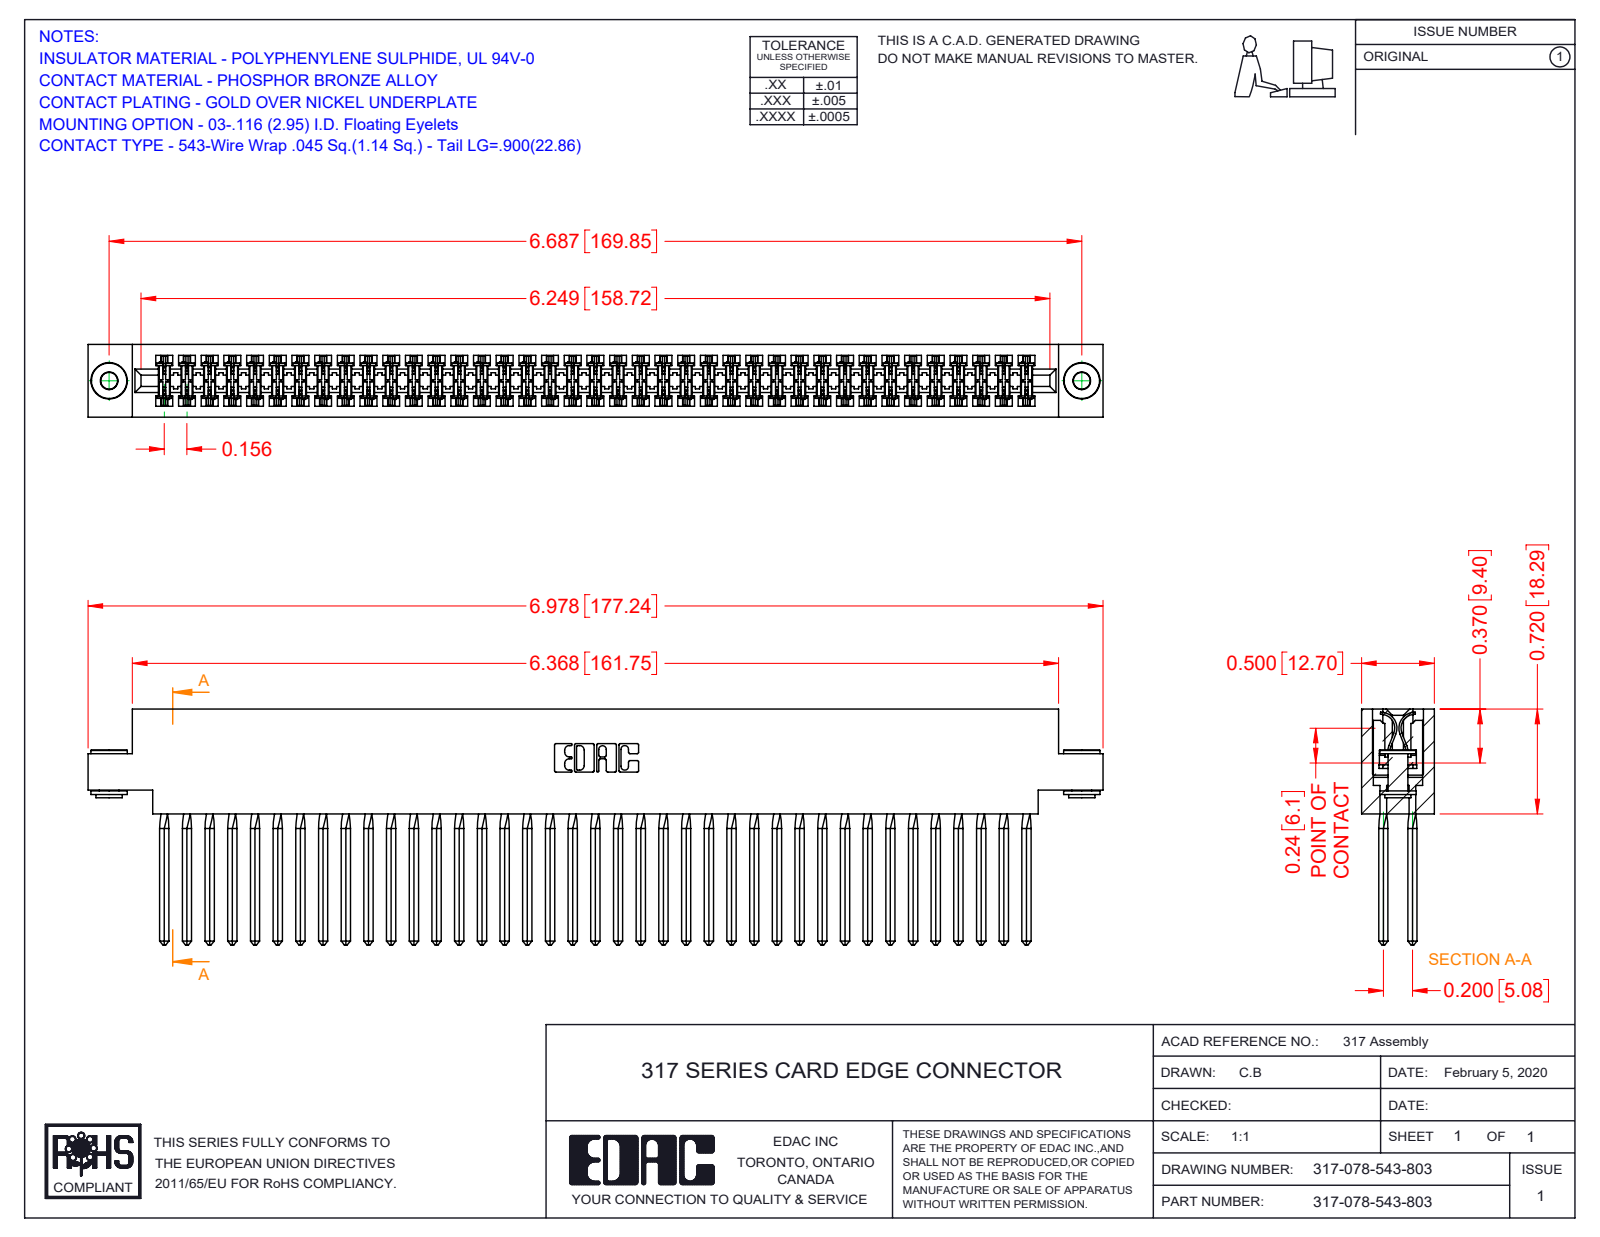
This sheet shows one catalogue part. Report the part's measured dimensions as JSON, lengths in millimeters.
{"part_name": "345-250-002_345-250-002-102; 317-078-543-803; 317-290-001_543; 317 Part_.156 Dia - TH", "step_written_by": "SolidWorks 2016 (CONFIG_CONTROL_DESIGN)", "units": "millimeters", "bodies": {"solids": 81, "faces": 7082, "planar": 5762, "cylindrical": 1000, "other": 320}, "overall_size": [177.2, 41.1, 12.7], "volume_mm3": 30050, "surface_area_mm2": 45680, "round_holes": [[2.9, 2], [4, 2]], "round_bosses_or_shafts": [[6.4, 2], [4.6, 2], [3.5, 2]], "partial_cylinders_radius": [[0.4, 156], [0.3, 22], [0.2, 6], [0.8, 6], [0.7, 3], [2.4, 2], [2.5, 2], [2.8, 2]], "face_to_face_distances": [12.7, 1.9, 10.8, 8.9, 2.8, 5, 2.4, 5.1, 2.9, 3.3], "hole_center_spacings": [169.8]}
